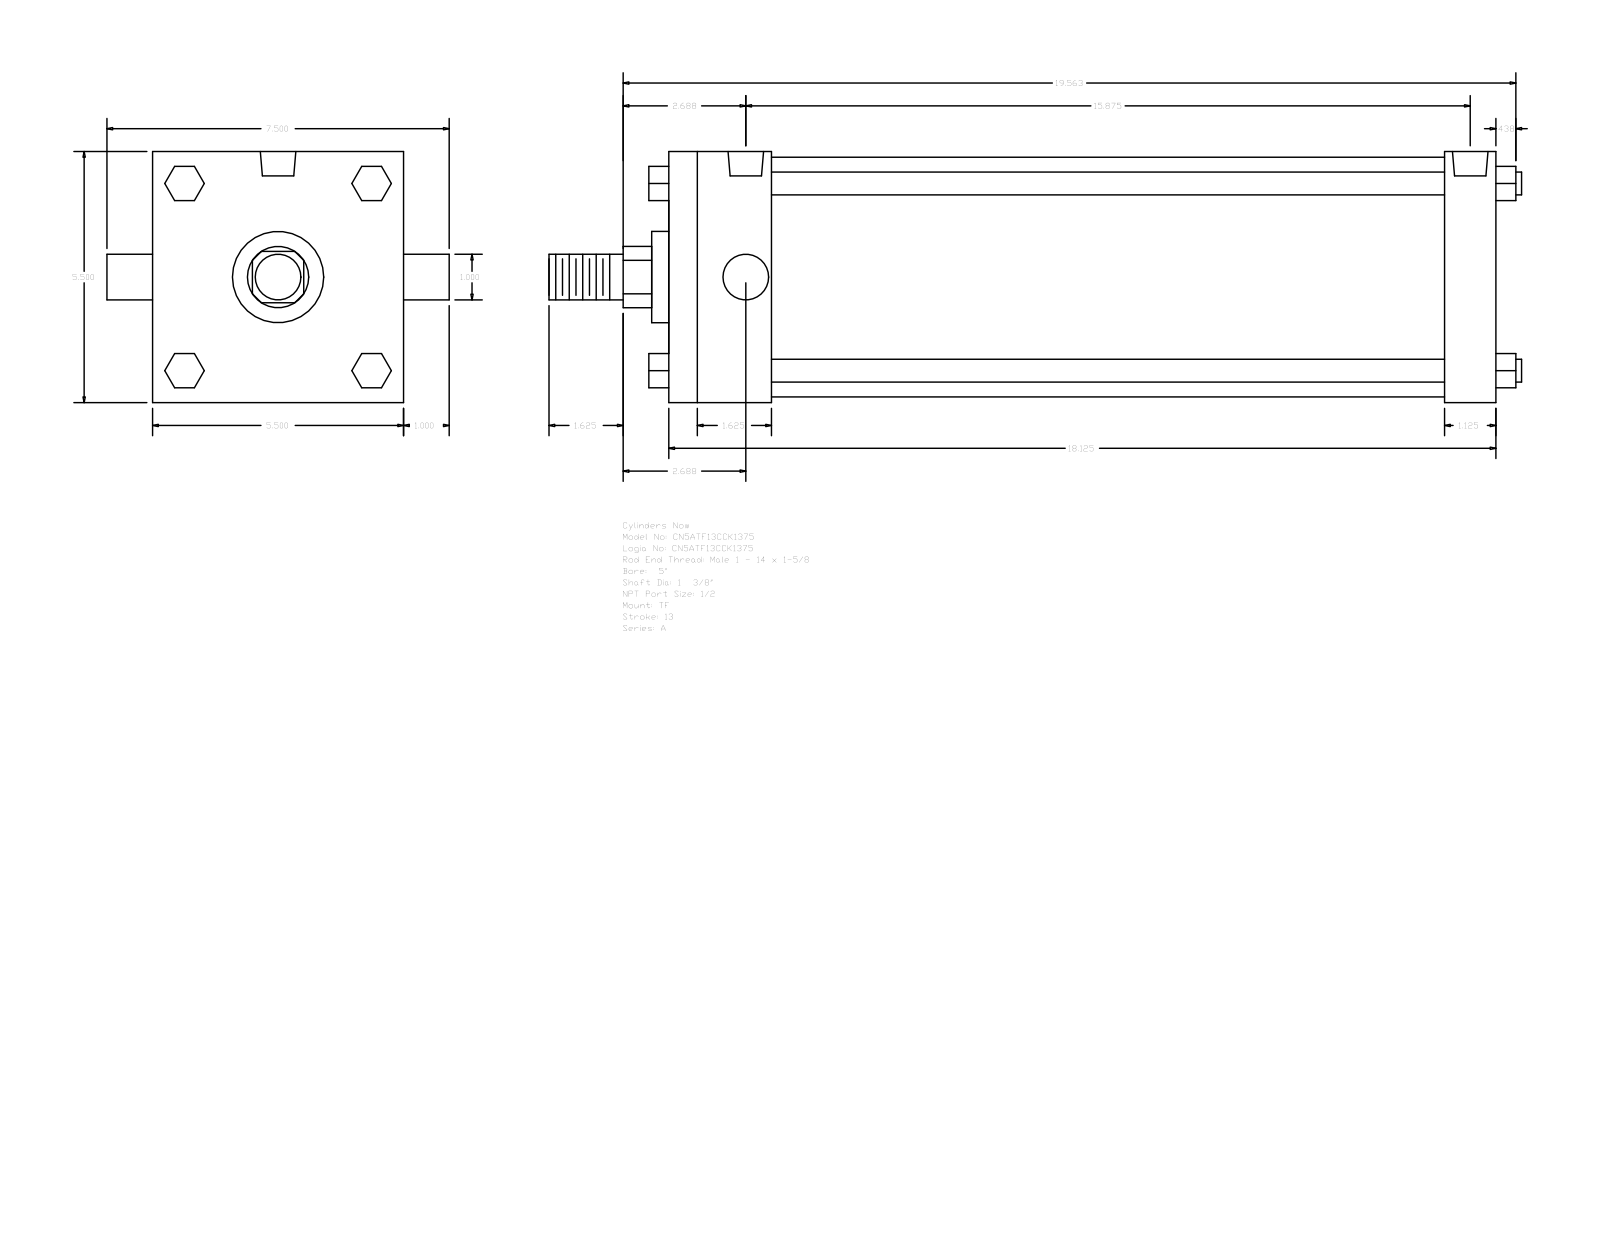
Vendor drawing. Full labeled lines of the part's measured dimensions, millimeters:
Part name (STEP PRODUCT): A_TF__0500_1.375
STEP written by: GSSL Pune (CONFIG_CONTROL_DESIGN)
Units: millimetres
Bodies: 0 solids, 120 faces (92 planar, 28 cylindrical, 0 other)
Overall size (bounding box): 541.34 × 190.5 × 139.7
Round holes (diameter × count): ⌀8.73 ×3, ⌀19.77 ×2
Round bosses / shafts (diameter × count): ⌀12.7 ×4, ⌀25.4 ×2, ⌀133.35 ×1, ⌀50.8 ×1, ⌀34.92 ×1
Partial cylindrical surfaces — rounded edges, fillets, slot ends (radius × count): R17.06 ×1
Main face-to-face distances: 139.7, 460.37, 57.15, 431.8, 28.57, 374.65, 403.22, 19.05, 52.07, 90.18
Hole centre spacings: 2.39, 400.84, 398.45, 403.23
